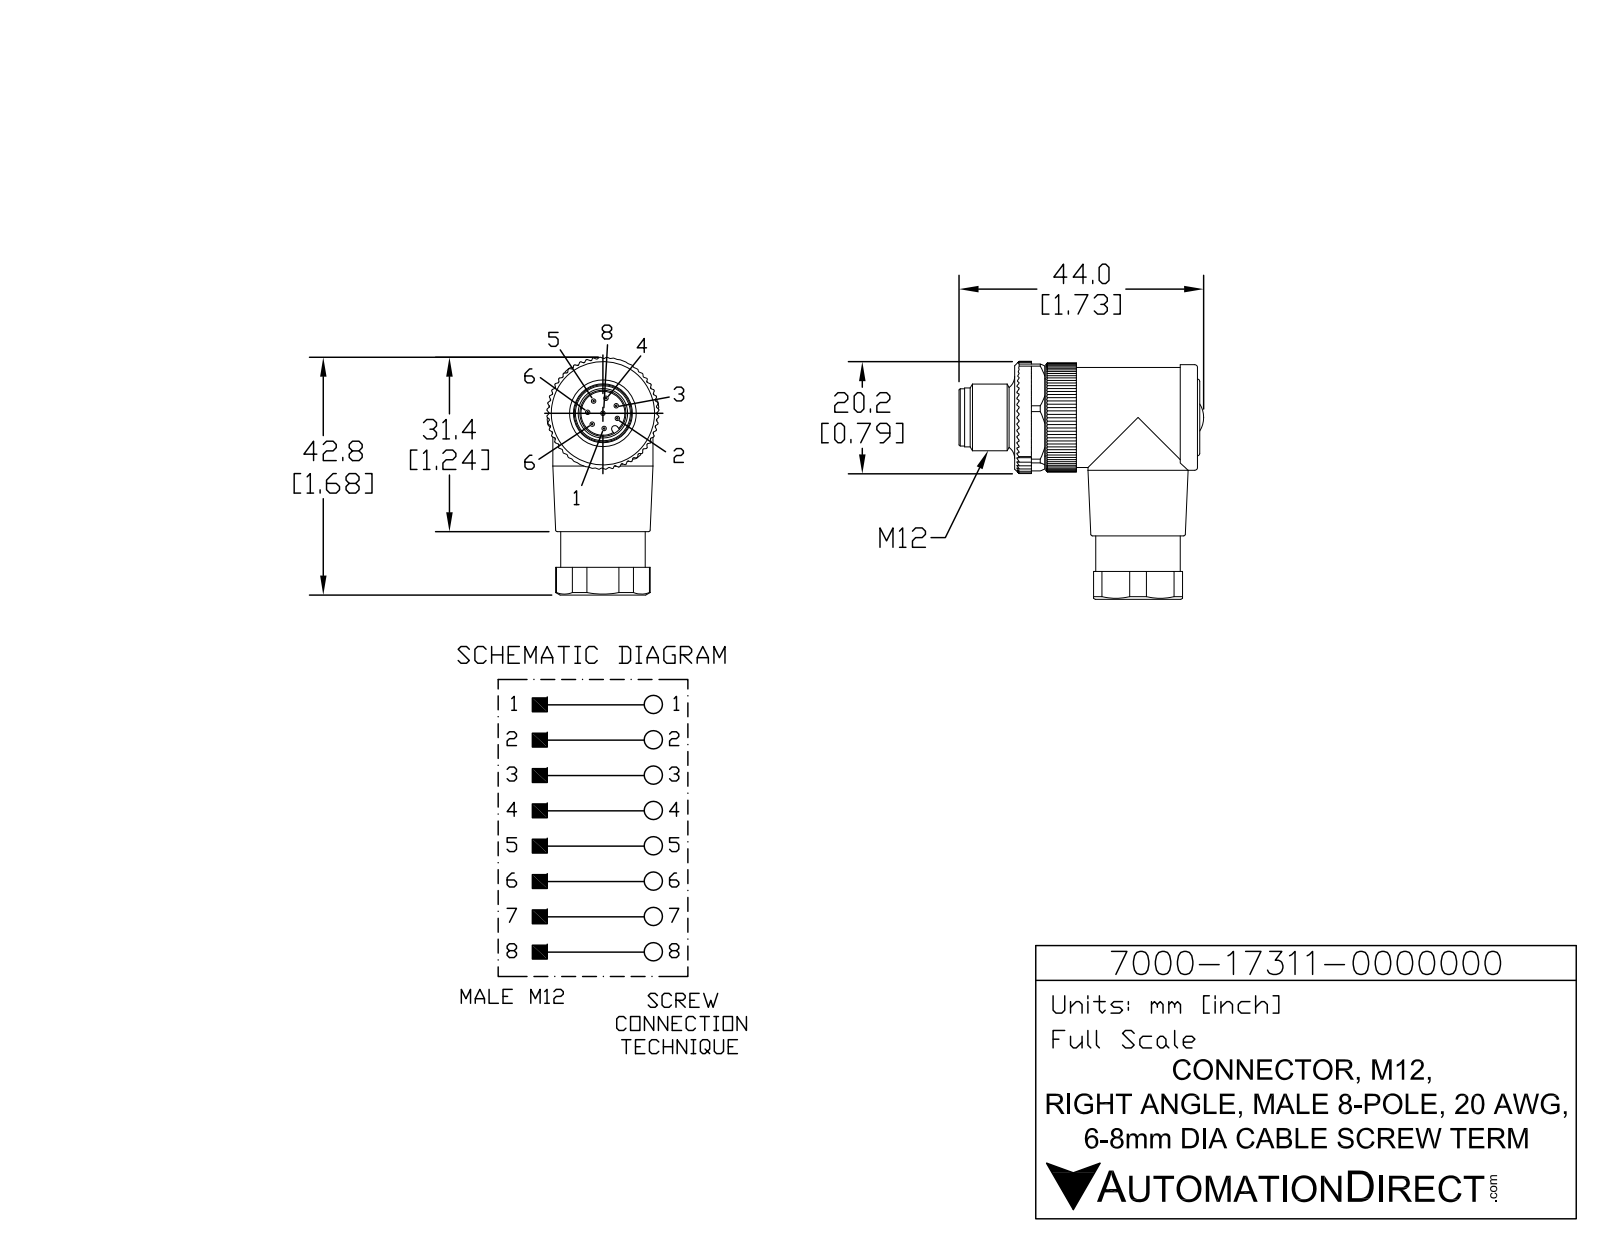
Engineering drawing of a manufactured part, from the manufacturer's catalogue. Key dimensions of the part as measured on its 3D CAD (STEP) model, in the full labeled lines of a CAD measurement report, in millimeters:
Part name (STEP PRODUCT): 7000-17311-0000000
STEP written by: SolidWorks 2019 (AUTOMOTIVE_DESIGN)
Units: millimetres
Bodies: 1 solid, 671 faces (355 planar, 266 cylindrical, 50 other)
Overall size (bounding box): 44 × 42.8 × 20.2
Volume: 15 100 mm³ · Surface area: 5 036 mm²
Round holes (diameter × count): ⌀8.3 ×1
Round bosses / shafts (diameter × count): ⌀0.8 ×8, ⌀18 ×2, ⌀19 ×1, ⌀15.2 ×1, ⌀13.9 ×1, ⌀12 ×1, ⌀10.6 ×1, ⌀10.3 ×1
Partial cylindrical surfaces — rounded edges, fillets, slot ends (radius × count): R0.2 ×98, R0.6 ×1, R8.5 ×1, R9.8 ×1, R10.1 ×1
Main face-to-face distances: 27.3, 27.5, 5.4, 5.6, 32.9, 17.4, 17.3, 16, 18, 3.1
